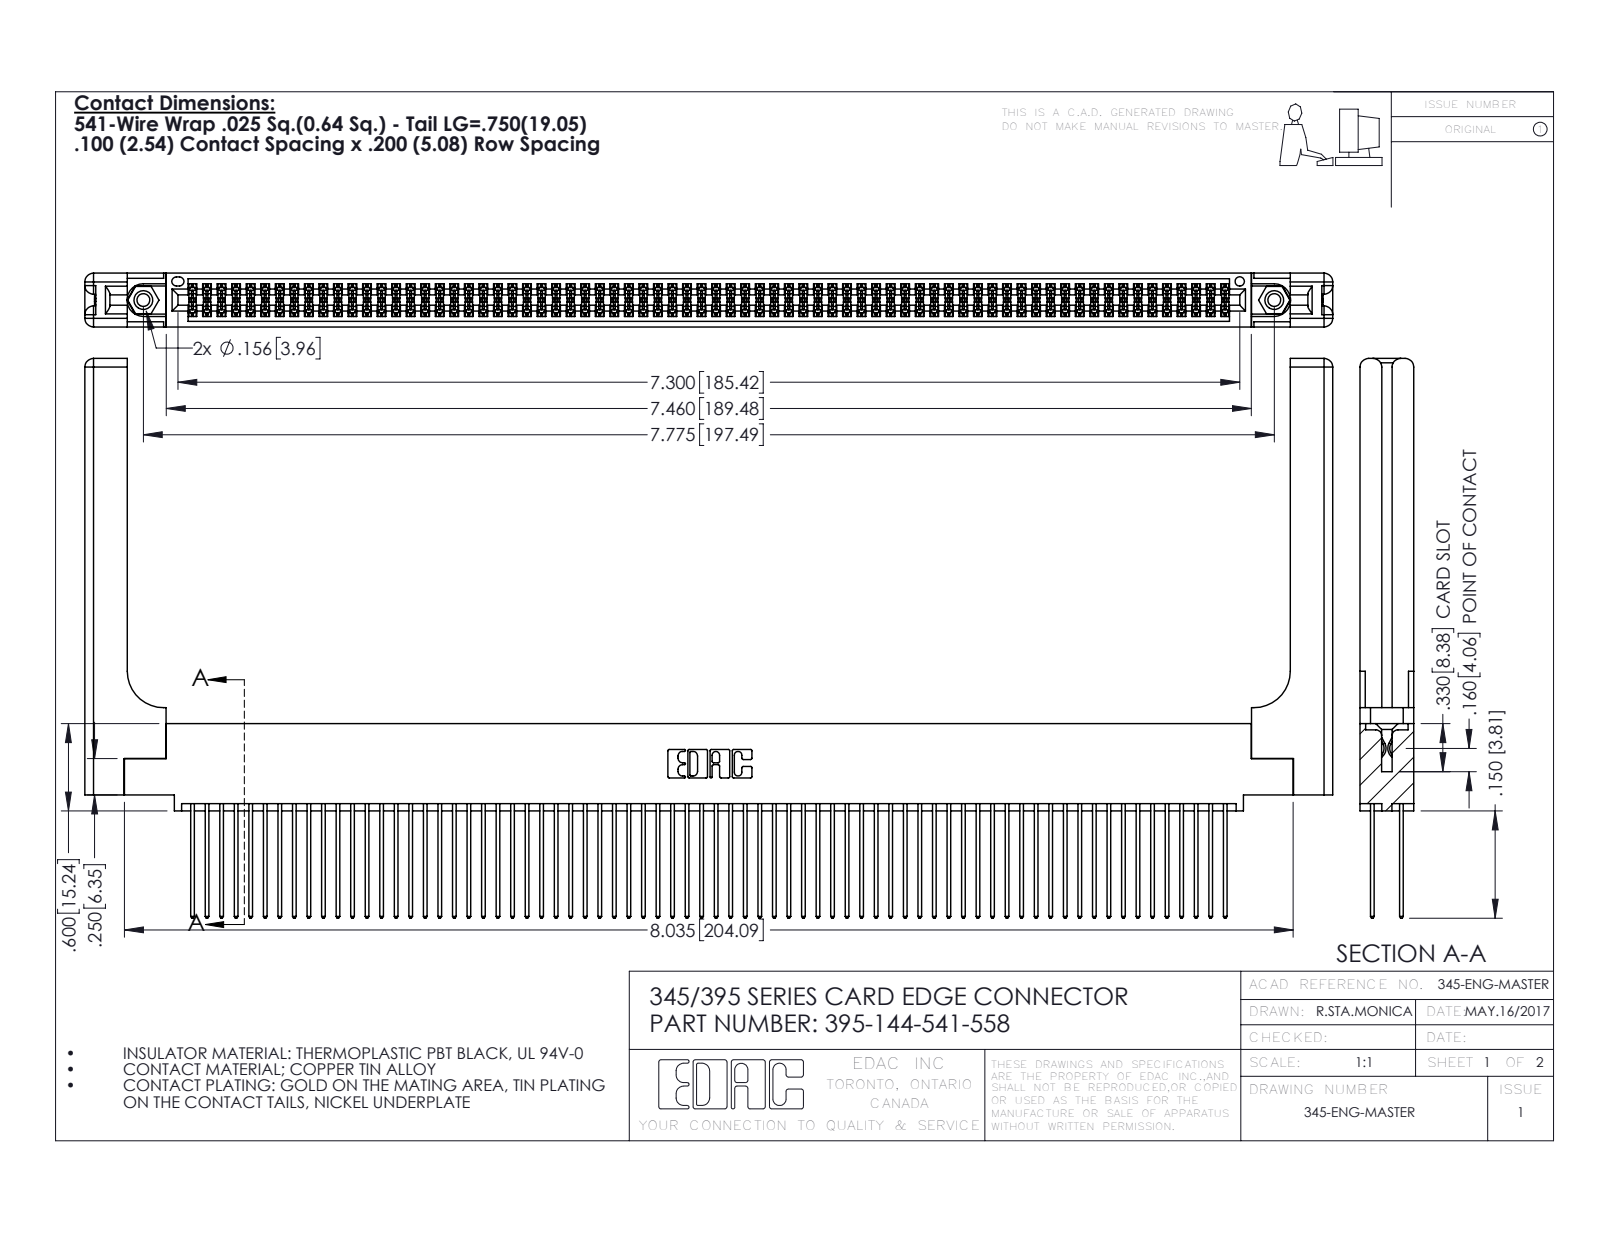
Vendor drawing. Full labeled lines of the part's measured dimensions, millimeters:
Part name (STEP PRODUCT): 345 Part_0.110 Offset - 0.156 Dia-TH; 345-250-001_345-250-001-102; 395-144-541-558; 345-292-001_345-293-141 (+1 more)
STEP written by: SolidWorks 2016 (CONFIG_CONTROL_DESIGN)
Units: millimetres
Bodies: 149 solids, 7586 faces (4984 planar, 2542 cylindrical, 60 other)
Overall size (bounding box): 217.9 × 97.7 × 9.4
Volume: 30 680 mm³ · Surface area: 42 430 mm²
Round holes (diameter × count): ⌀2.3 ×2, ⌀3.2 ×2, ⌀4 ×2, ⌀1.6 ×1
Round bosses / shafts (diameter × count): ⌀3.9 ×2
Partial cylindrical surfaces — rounded edges, fillets, slot ends (radius × count): R0.2 ×216, R0.3 ×144, R0.3 ×22, R1.5 ×16, R0.2 ×6, R0.8 ×6, R0.7 ×3, R0.4 ×2
Main face-to-face distances: 1.8, 7.6, 2.5, 6.9, 0.6, 5.1, 9.4, 5.7, 4.4, 3.8
Hole centre spacings: 6.9, 191.5, 197.5
